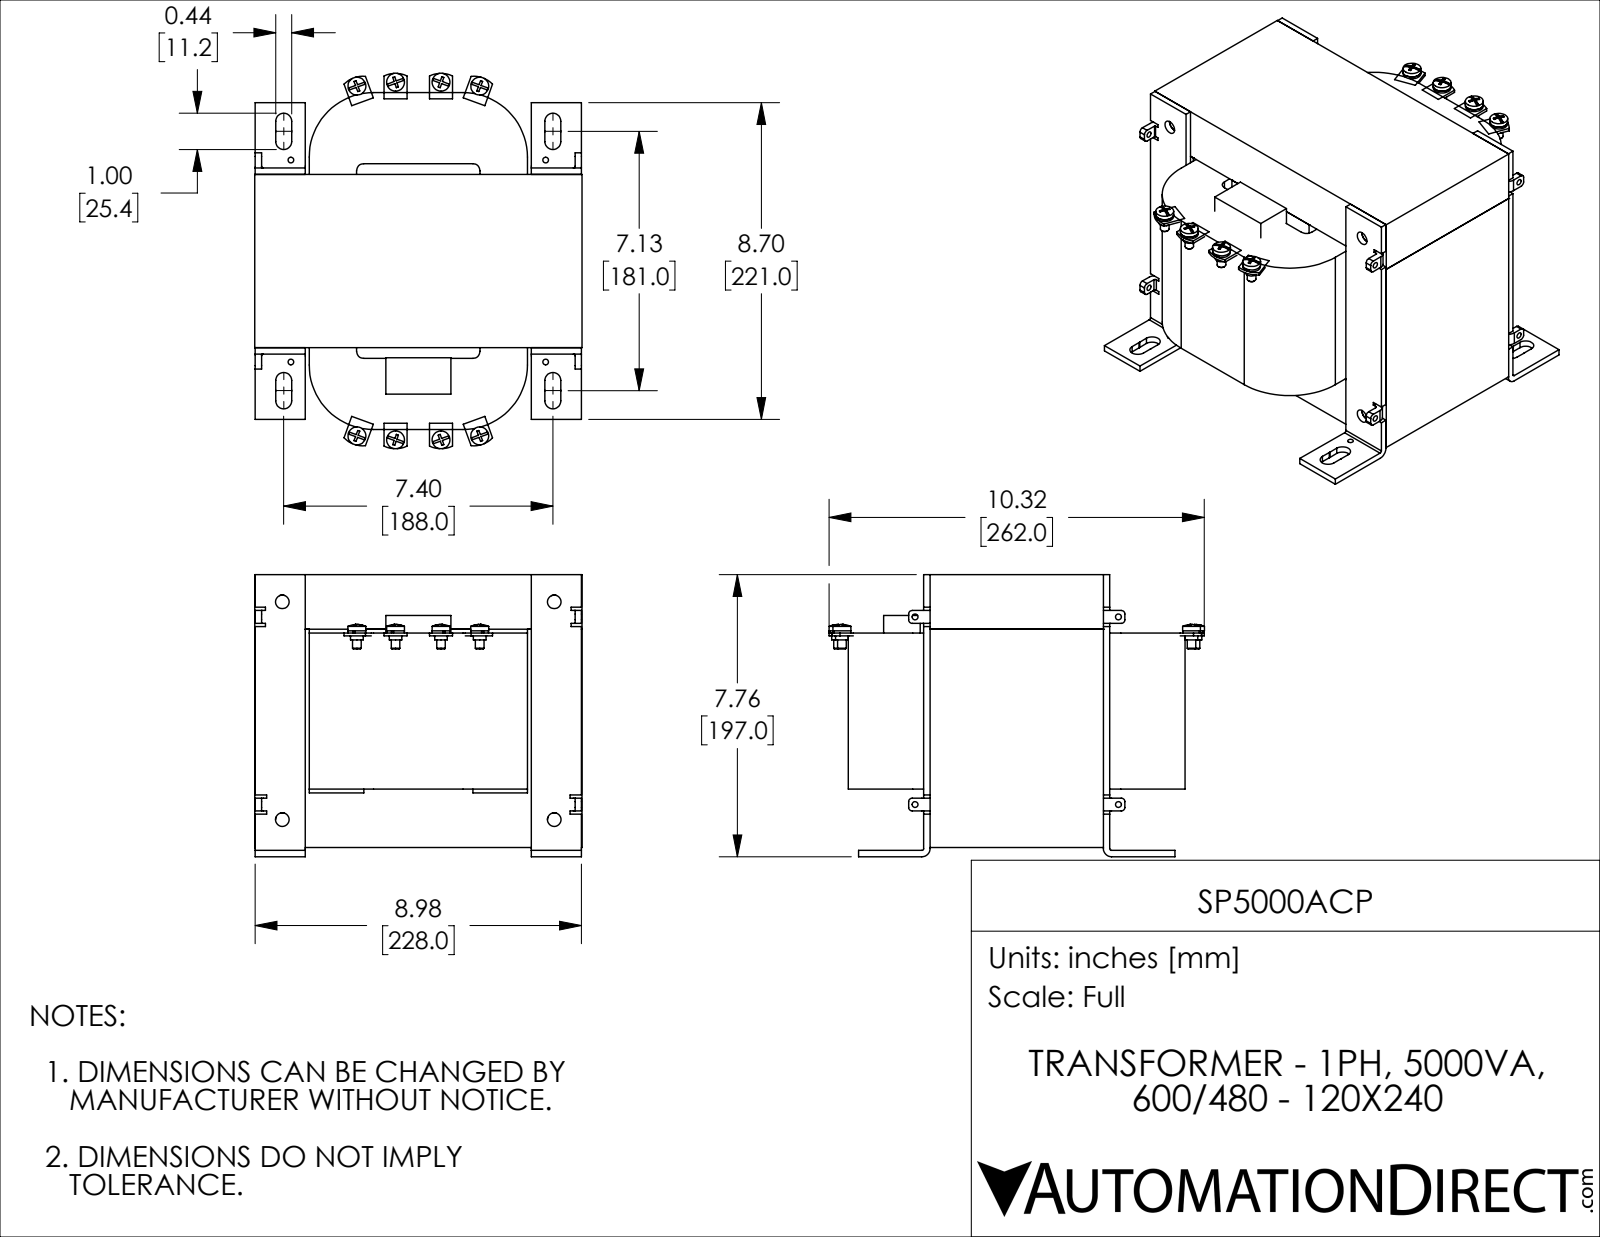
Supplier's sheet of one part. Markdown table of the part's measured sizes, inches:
| quantity | value |
| --- | --- |
| part name | SP5000ACP |
| STEP written by | SolidWorks 2018 (AUTOMOTIVE_DESIGN) |
| units | inches |
| bodies | 32 solids, 632 faces (348 planar, 232 cylindrical, 52 other) |
| overall size | 10.322 × 9 × 7.756 |
| volume | 416.5 in³ |
| surface area | 874.6 in² |
| round holes (diameter × count) | 0.25 × 8, 0.276 × 8, 0.157 × 4, 0.161 × 4, 0.374 × 4 |
| round bosses / shafts (diameter × count) | 0.492 × 8, 0.484 × 8, 0.346 × 8, 0.236 × 8 |
| partial cylindrical surfaces (radius × count) | 0.098 × 8, 0.22 × 8, 0.732 × 8, 0.05 × 6, 0.227 × 6, 0.02 × 4, 0.197 × 4, 0.221 × 4 |
| main face-to-face distances | 1.5, 6, 7.5, 1.604, 5.896, 4.764, 3, 4.5, 0.104, 4.396 |
| hole center spacings | 1.07, 2.316, 2.724, 3.587, 4.65, 5.576, 7.797, 8.212 |
